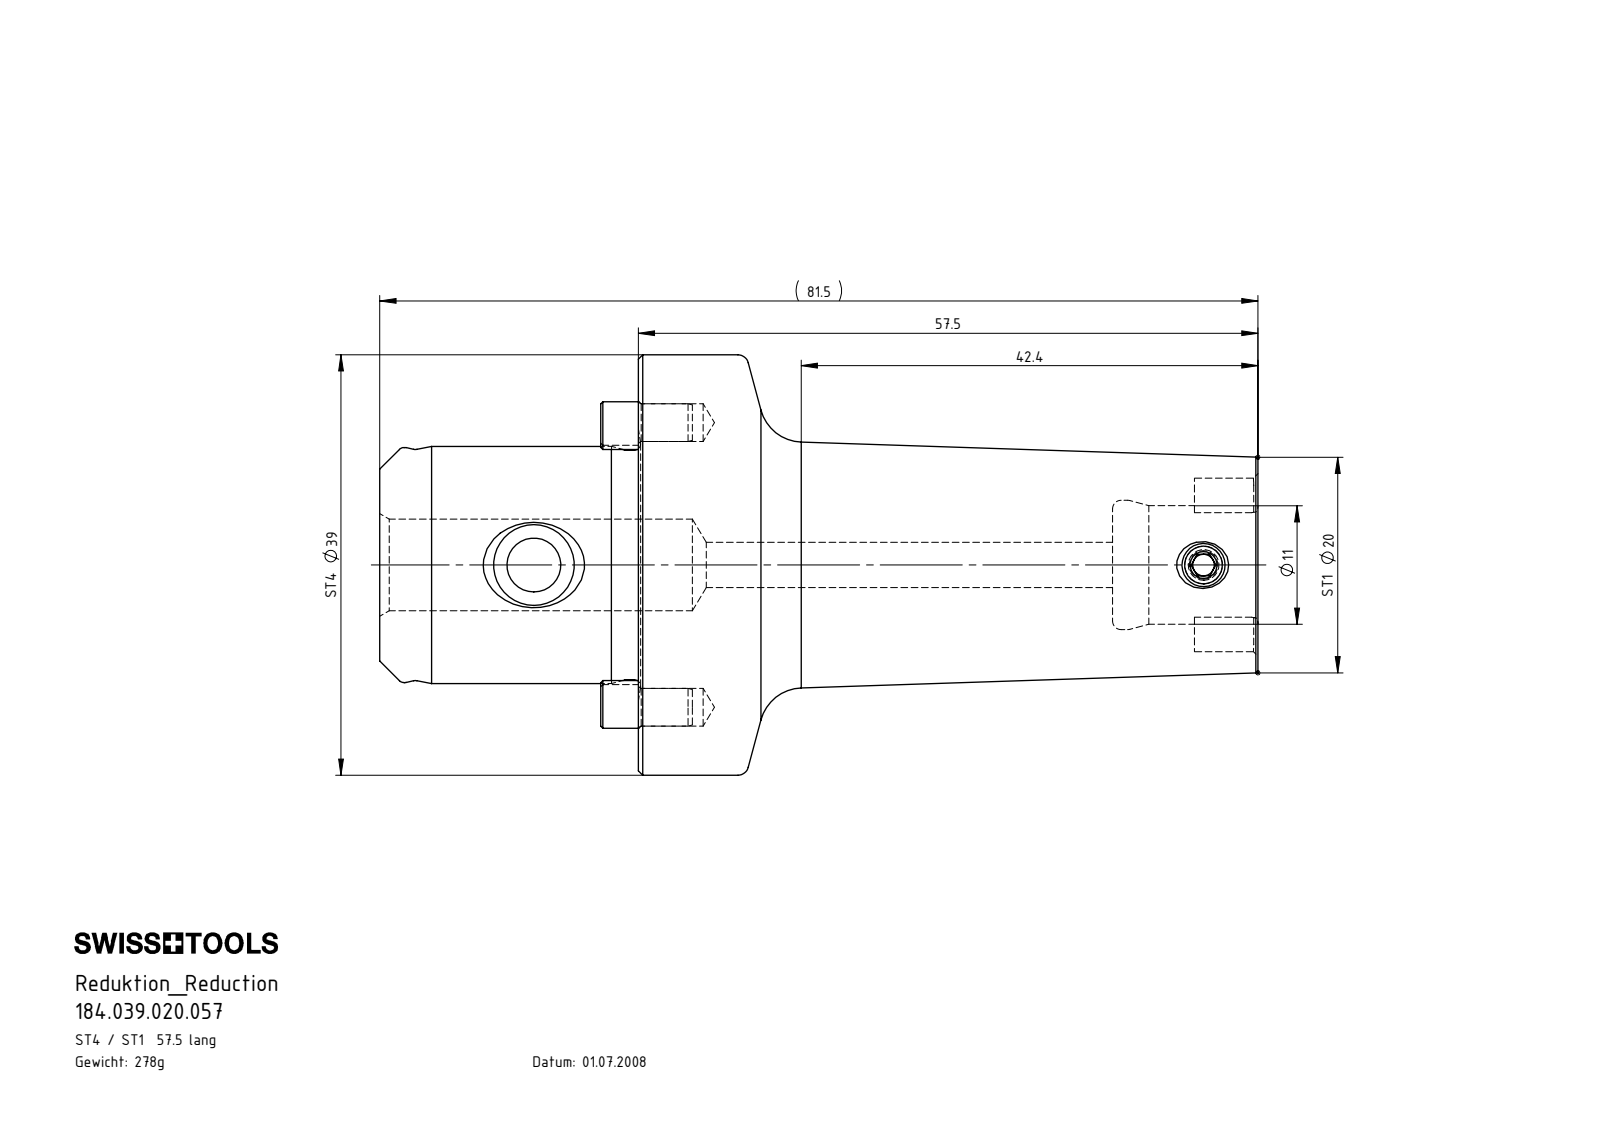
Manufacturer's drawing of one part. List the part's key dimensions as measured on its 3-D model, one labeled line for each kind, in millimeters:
Part name (STEP PRODUCT): ST1-ER1.001.005_A; ST4-ST1.K01.057; ST4-ER2.001.009_A; ST4-ST1.K01.057_A
STEP written by: SolidWorks 2015 (CONFIG_CONTROL_DESIGN)
Units: millimetres
Bodies: 4 solids, 162 faces (26 planar, 45 cylindrical, 91 other)
Overall size (bounding box): 81.5 × 39 × 39
Volume: 35 380 mm³ · Surface area: 10 470 mm²
Round holes (diameter × count): ⌀3.5 ×3, ⌀4.2 ×1, ⌀5 ×1, ⌀8.5 ×1, ⌀11 ×1, ⌀12 ×1
Round bosses / shafts (diameter × count): ⌀39 ×1, ⌀22 ×1, ⌀21.8 ×1, ⌀21.3 ×1, ⌀4 ×1
Partial cylindrical surfaces — rounded edges, fillets, slot ends (radius × count): R0.5 ×4, R1.3 ×2, R3.48 ×2, R11.05 ×2
Main face-to-face distances: 24, 81.5, 57.5, 68, 44, 13.5, 20.5, 3.5, 47.5, 61
Hole centre spacings: 13.2, 26.4, 62.15
